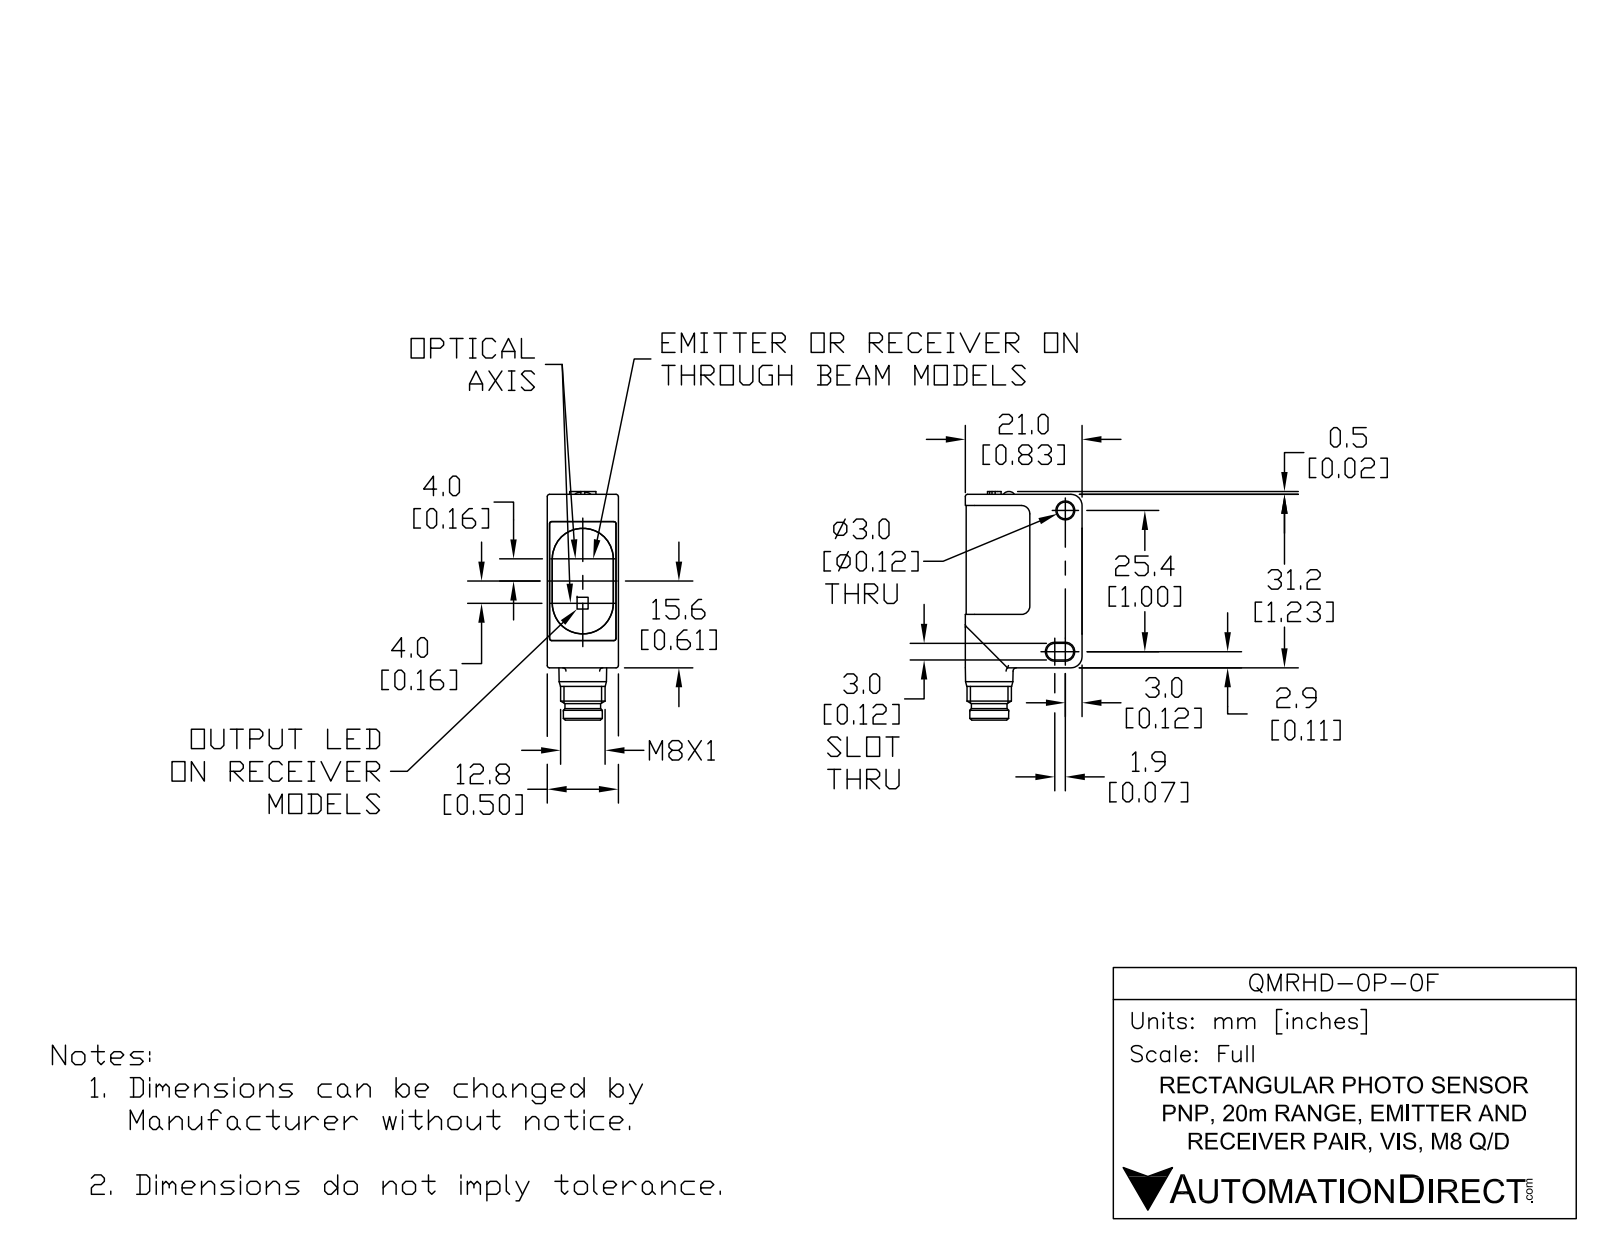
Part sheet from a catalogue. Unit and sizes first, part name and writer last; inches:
Units: inches
Overall size (bounding box): 1.619 × 0.827 × 0.504
Round holes (diameter × count): ⌀0.118 ×3, ⌀0.228 ×1
Round bosses / shafts (diameter × count): ⌀0.039 ×4, ⌀0.138 ×2, ⌀0.315 ×1, ⌀0.276 ×1, ⌀0.252 ×1
Partial cylindrical surfaces — rounded edges, fillets, slot ends (radius × count): R0.016 ×10, R0.02 ×9, R0.059 ×6, R0.024 ×4, R0.039 ×4, R0.006 ×2, R0.044 ×2, R0.065 ×2
Main face-to-face distances: 0.498, 0.02, 0.504, 0.11, 0.016, 0.492, 0.488, 0.482, 0.059, 0.711
Hole centre spacings: 0.04, 0.205, 0.245
Volume: 0.474 in³ · Surface area: 7.749 in²
Bodies: 7 solids, 272 faces (125 planar, 100 cylindrical, 47 other)
Part name (STEP PRODUCT): QMRHD-0P-0F
STEP written by: SolidWorks 2017 (AUTOMOTIVE_DESIGN)
